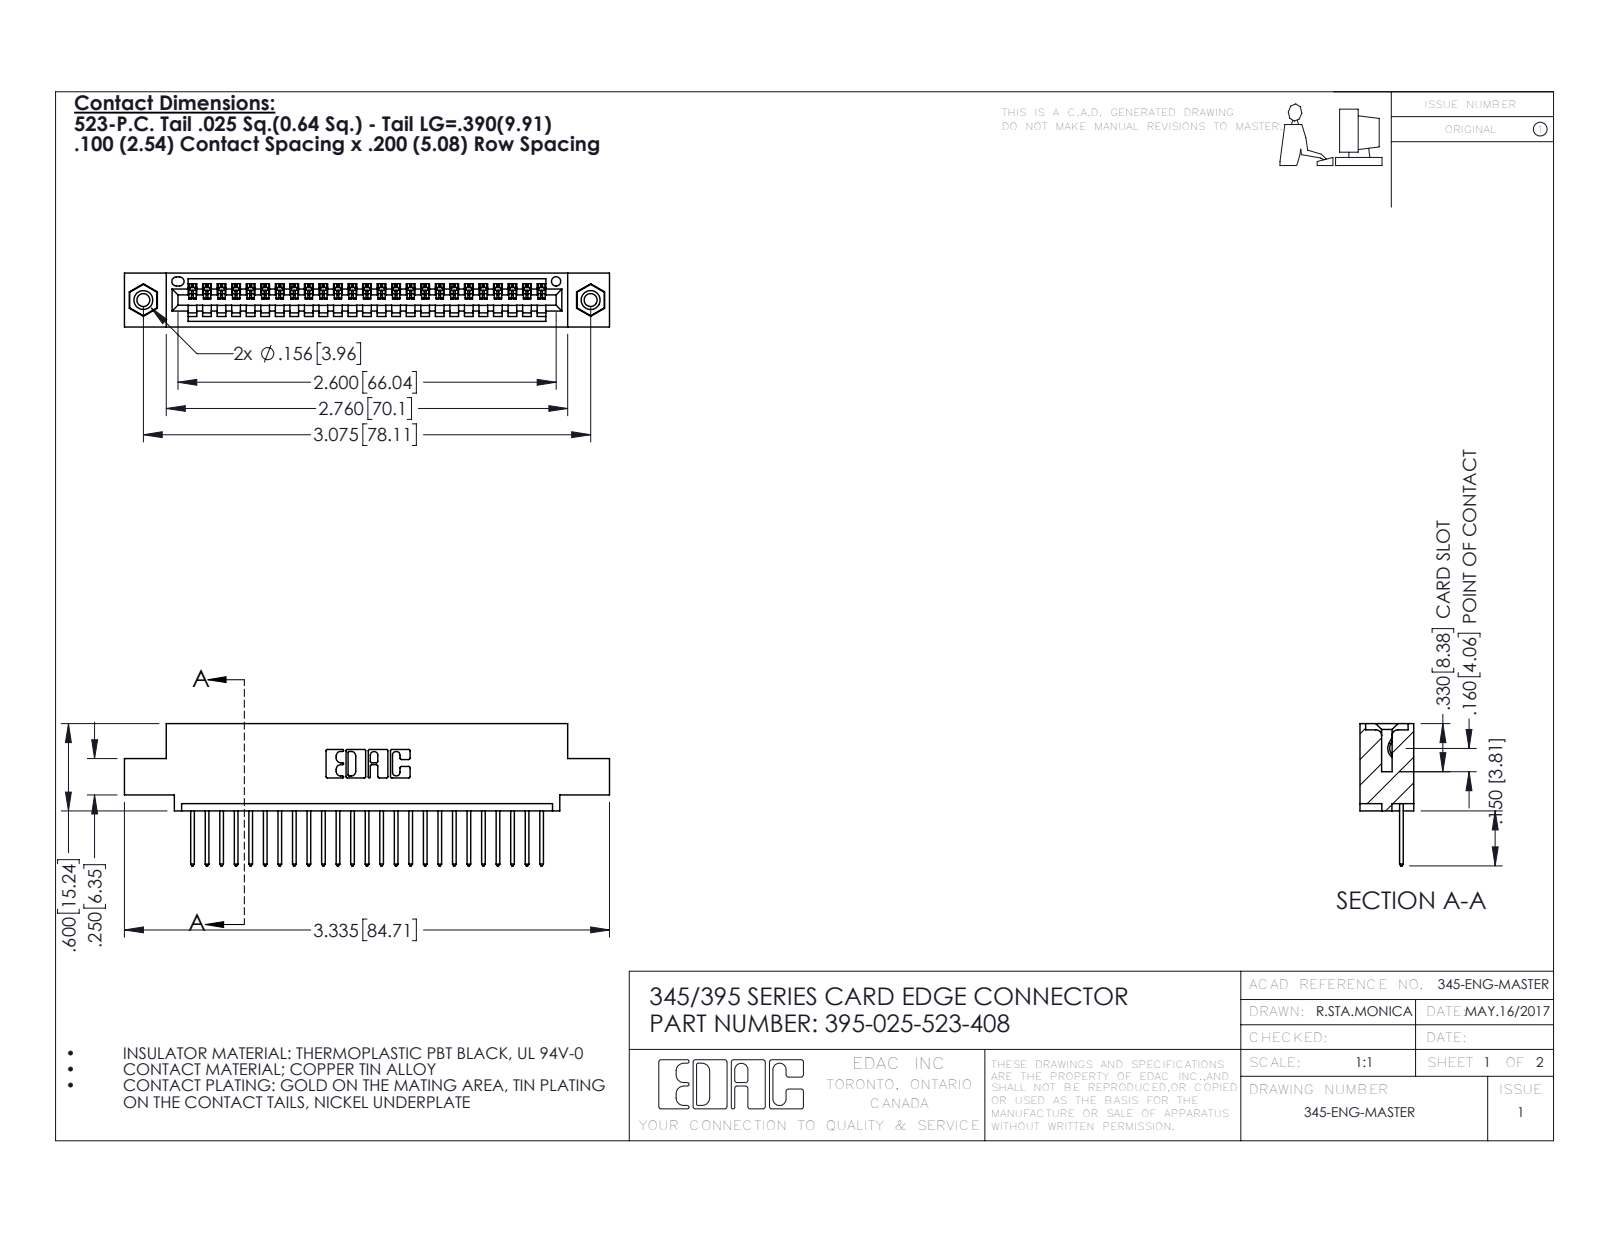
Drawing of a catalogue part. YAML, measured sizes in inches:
part_name: "345-250-001_345-250-003-102; 345-292-001_345-293-123; 345 Part_0.110 Offset - 0.156 Dia-TI; 395-025-523-408"
step_written_by: "SolidWorks 2016 (CONFIG_CONTROL_DESIGN)"
units: inches
bodies: {solids: 28, faces: 1640, planar: 1116, cylindrical: 508, other: 16}
overall_size: [3.335, 0.977, 0.37]
volume: 0.477
surface_area: 15.94
round_holes:
  - {diameter: 0.089, count: 2}
  - {diameter: 0.125, count: 2}
  - {diameter: 0.156, count: 2}
  - {diameter: 0.064, count: 1}
round_bosses_or_shafts:
  - {diameter: 0.155, count: 2}
partial_cylinders:
  - {radius: 0.006, count: 50}
  - {radius: 0.01, count: 50}
  - {radius: 0.01, count: 22}
  - {radius: 0.007, count: 6}
  - {radius: 0.031, count: 6}
  - {radius: 0.026, count: 3}
  - {radius: 0.031, count: 2}
  - {radius: 0.04, count: 2}
face_to_face_distances: [0.072, 0.298, 0.37, 0.2, 0.098, 0.272, 0.025, 0.225, 0.149, 0.072]
hole_center_spacings: [0.27, 2.84, 3.075]
